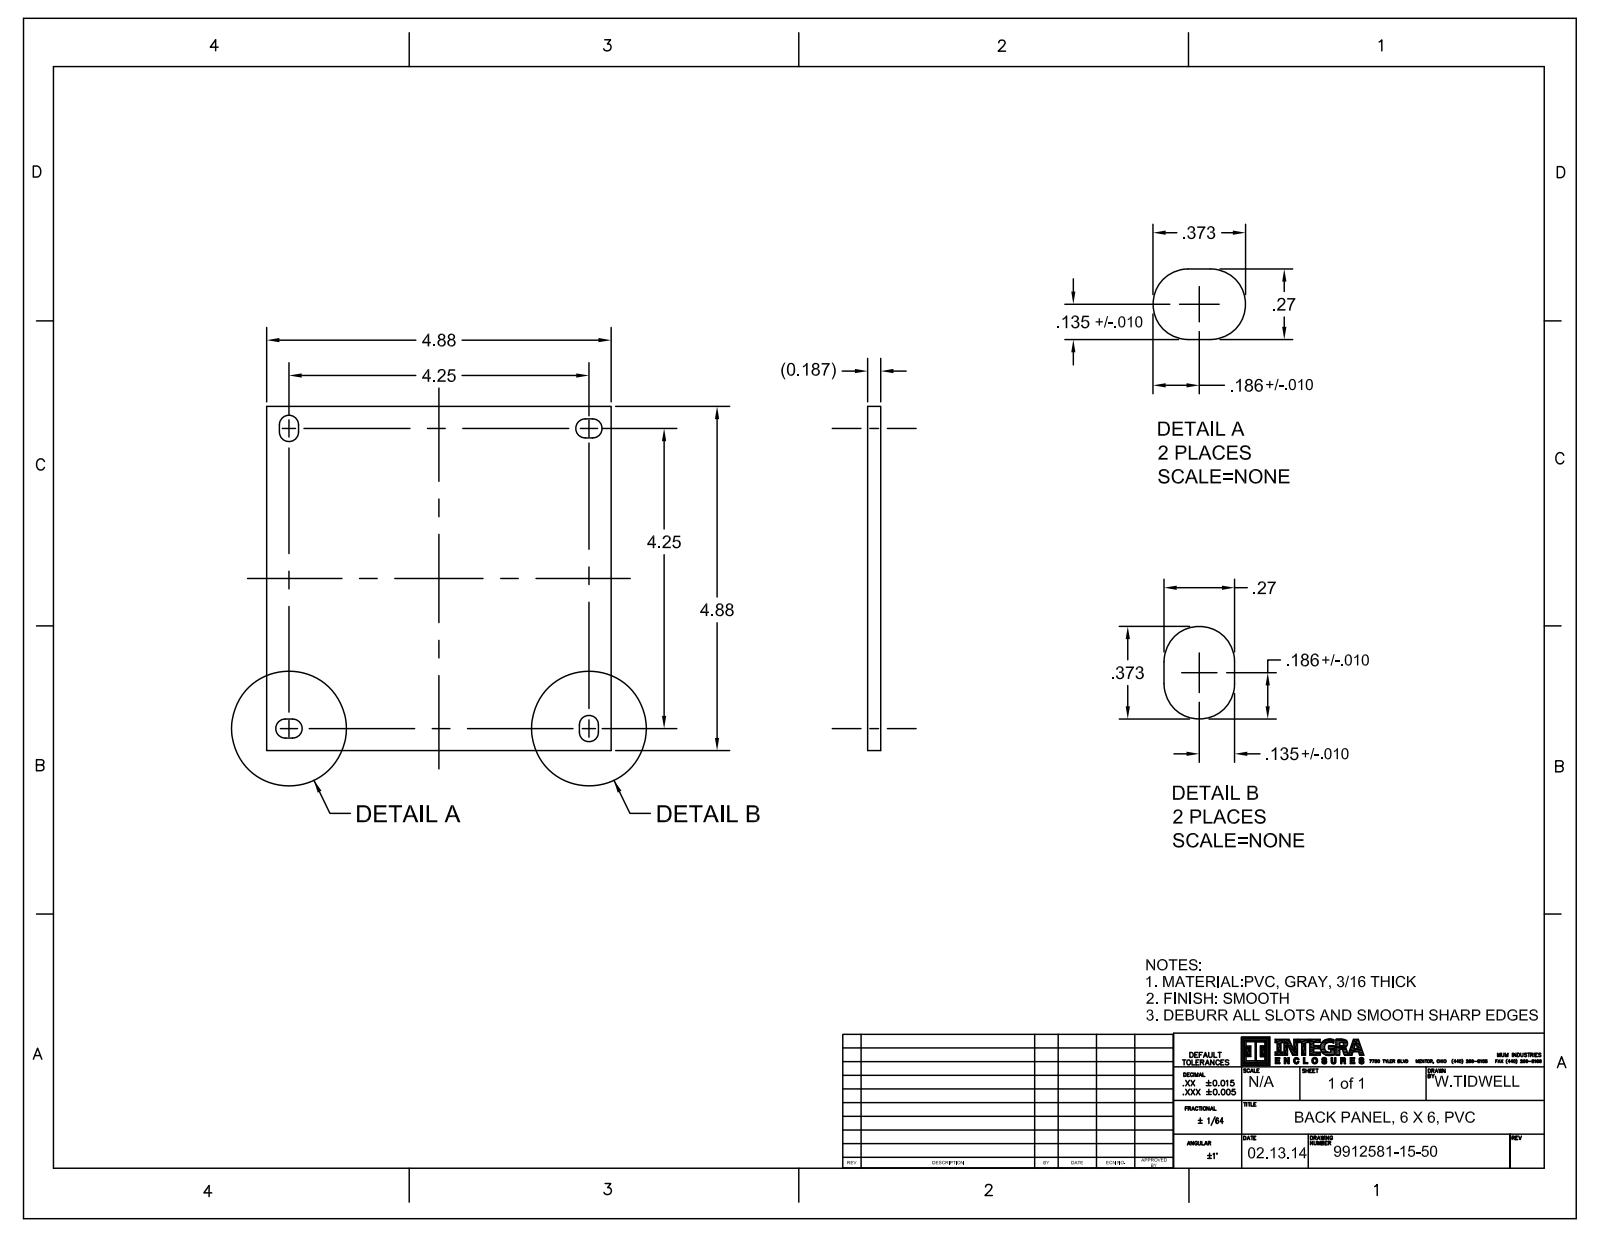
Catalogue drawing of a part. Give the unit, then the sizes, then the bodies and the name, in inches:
Units: inches
Overall size (bounding box): 4.88 × 4.88 × 0.63
Round bosses / shafts (diameter × count): ⌀0.373 ×4, ⌀0.19 ×4, ⌀0.149 ×4
Partial cylindrical surfaces — rounded edges, fillets, slot ends (radius × count): R0.125 ×8
Main face-to-face distances: 0.187, 4.88, 0.19, 0.44, 4.44, 4.69, 0.25, 4.25, 0.313, 0.5
Volume: 4.49 in³ · Surface area: 54.62 in²
Bodies: 5 solids, 514 faces (90 planar, 336 cylindrical, 88 other)
Part name (STEP PRODUCT): 9912581-15-50; 9912537-82-10; PVCBP66_ASM
STEP written by: CREO PARAMETRIC BY PTC INC, 2016050 (CONFIG_CONTROL_DESIGN)
